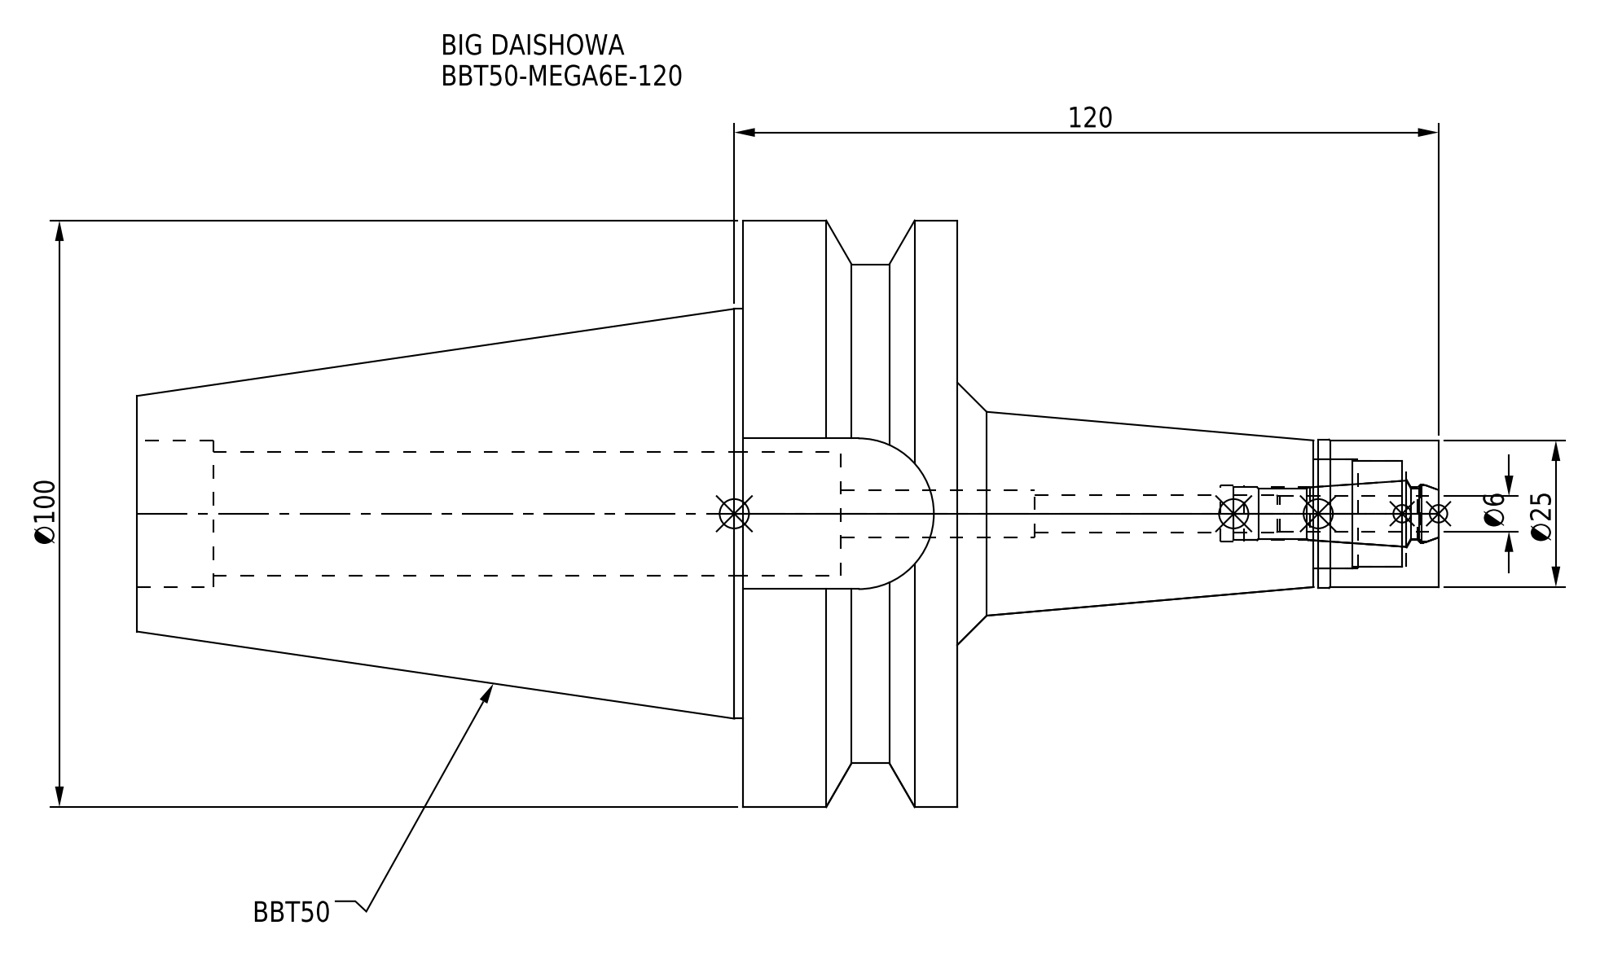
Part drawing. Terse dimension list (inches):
name: DXF_TEMP_ASSY_ASM_4_ASM.stp; MEN6_1.stp; BBT50ME06120-060_ASM.stp; BBT50-MEGA6E-120-060.stp (+3 more)
written by: SolidWorks 2019 (CONFIG_CONTROL_DESIGN)
unit: in
bodies: 2 solids, 81 faces (21 planar, 40 cylindrical, 20 other)
size: 8.732 × 3.937 × 3.937
volume: 30.83 in³; area: 101.1 in²
holes: 1× ⌀0.252, 1× ⌀0.315, 1× ⌀0.354, 1× ⌀0.378, 1× ⌀0.39, 1× ⌀0.709, 1× ⌀0.728, 1× ⌀0.835, 1× ⌀0.984
bosses: 1× ⌀3.937, 1× ⌀3.346, 1× ⌀2.75, 1× ⌀0.996
rounds: 1× R0.506
face distances: 1.437, 5.504, 4.067, 2.787, 1.012, 3.228, 4.665, 8.732, 0.657, 4.008
